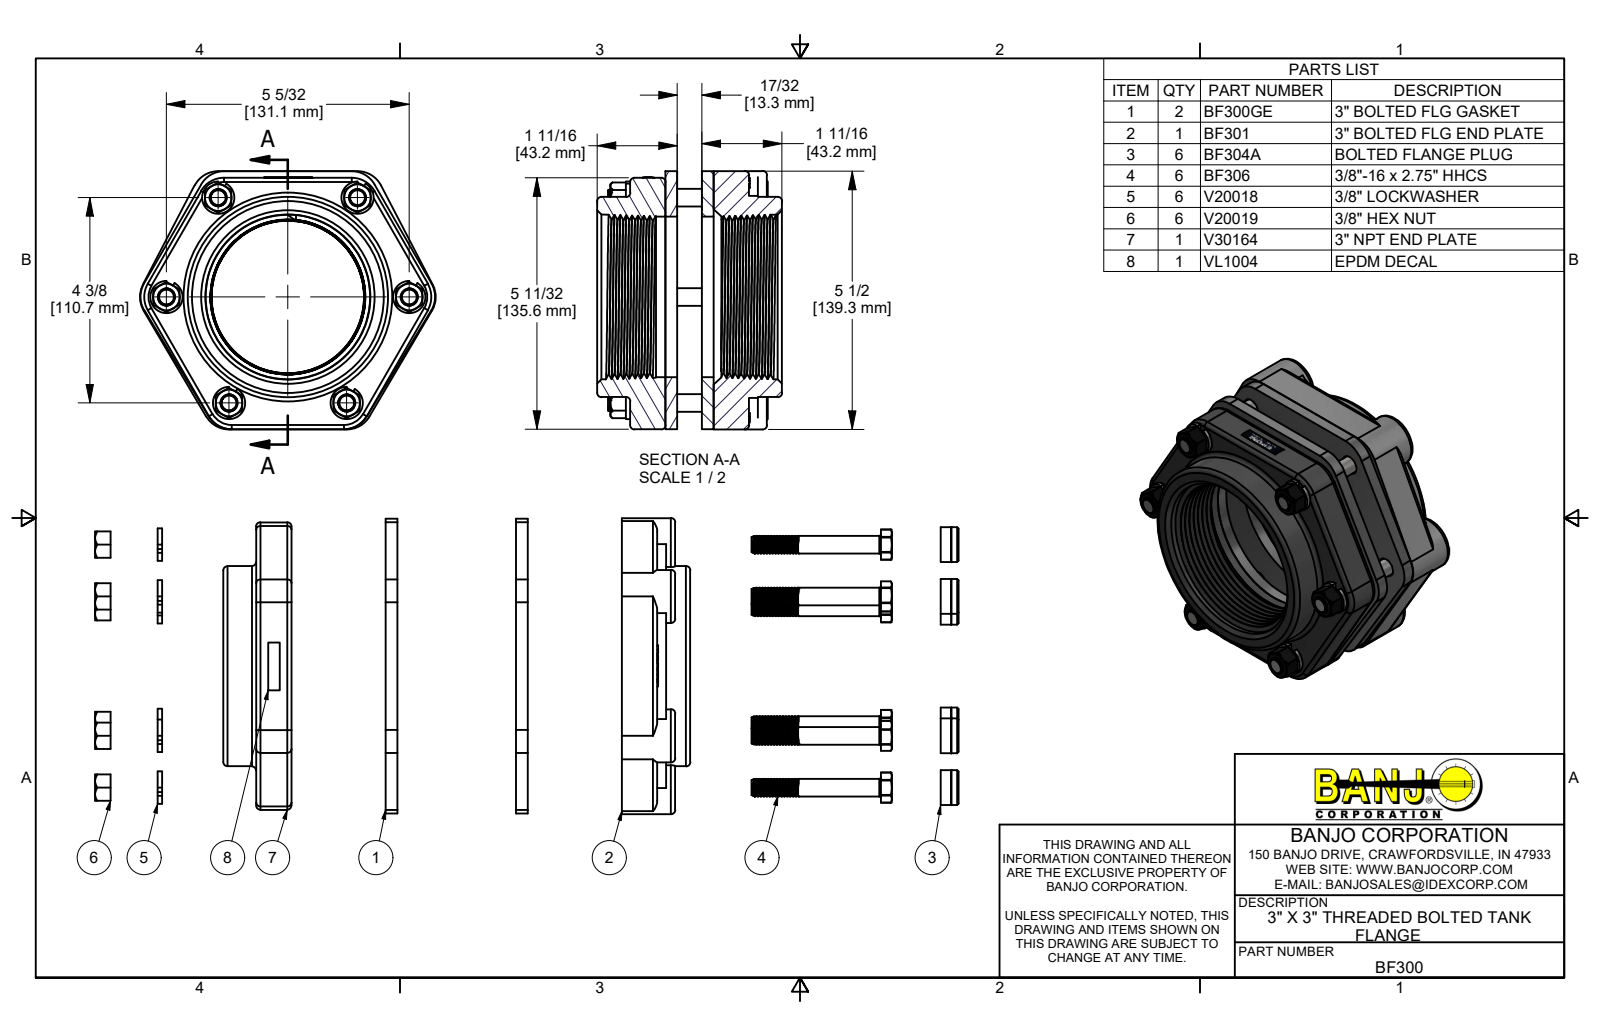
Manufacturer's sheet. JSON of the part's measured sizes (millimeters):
{"part_name": "BF300; BF301; BF300GE; V30164 (+5 more)", "step_written_by": "Autodesk Inventor 2019 (AUTOMOTIVE_DESIGN)", "units": "millimeters", "bodies": {"solids": 29, "faces": 1501, "planar": 460, "cylindrical": 469, "other": 572}, "overall_size": [159.6, 139.3, 99.6], "volume_mm3": 723700, "surface_area_mm2": 203500, "round_holes": [[7.8, 6], [9.8, 6], [10.3, 6], [10.3, 6], [10.4, 6], [18.2, 6], [19.1, 6], [86.6, 1]], "round_bosses_or_shafts": [[8.2, 90], [28.6, 6], [18.8, 6], [17.4, 6], [9.5, 6], [108, 1]], "partial_cylinders_radius": [[2.3, 18], [4.1, 12], [8.1, 6], [14.2, 6], [14.3, 6], [20.2, 2], [27.8, 2], [13.1, 1]], "face_to_face_distances": [6.4, 19.6, 26, 13.3, 19.1, 25.4, 38.7, 45, 17.8, 36.8], "hole_center_spacings": [60.5, 65.4, 65.5, 65.5, 66.4, 110.9, 112.8, 116.2]}
